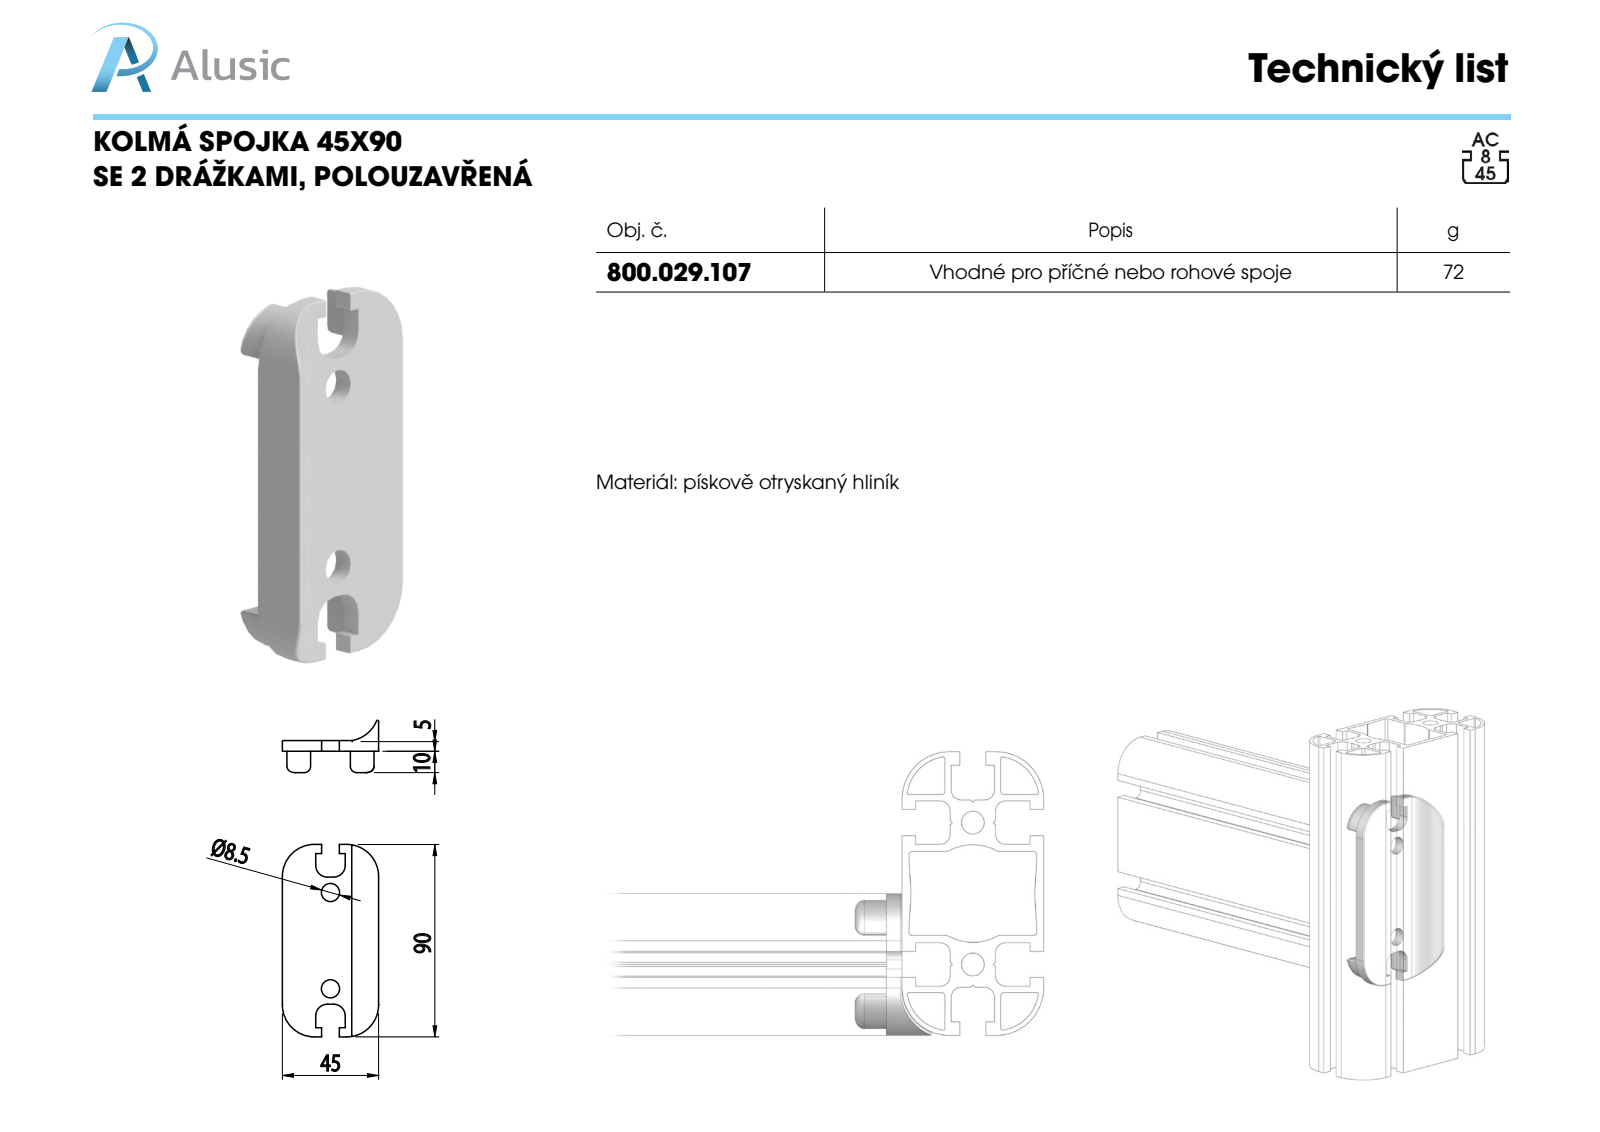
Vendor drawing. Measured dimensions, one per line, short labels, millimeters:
name: 800.029.107-2
written by: SolidWorks 2011 (CONFIG_CONTROL_DESIGN)
unit: mm
bodies: 1 solid, 101 faces (34 planar, 45 cylindrical, 22 other)
size: 90 × 45 × 24.48
volume: 23 619 mm³; area: 10 974 mm²
holes: 2× ⌀8.5
rounds: 12× R0.6, 4× R0.5, 4× R3, 4× R5.5, 4× R13.1, 4× R15, 1× R15.2
face distances: 5, 13.2, 31.8, 45, 18.6, 63.6, 15.6, 29.4, 2.4, 16.2
hole spacings: 45
